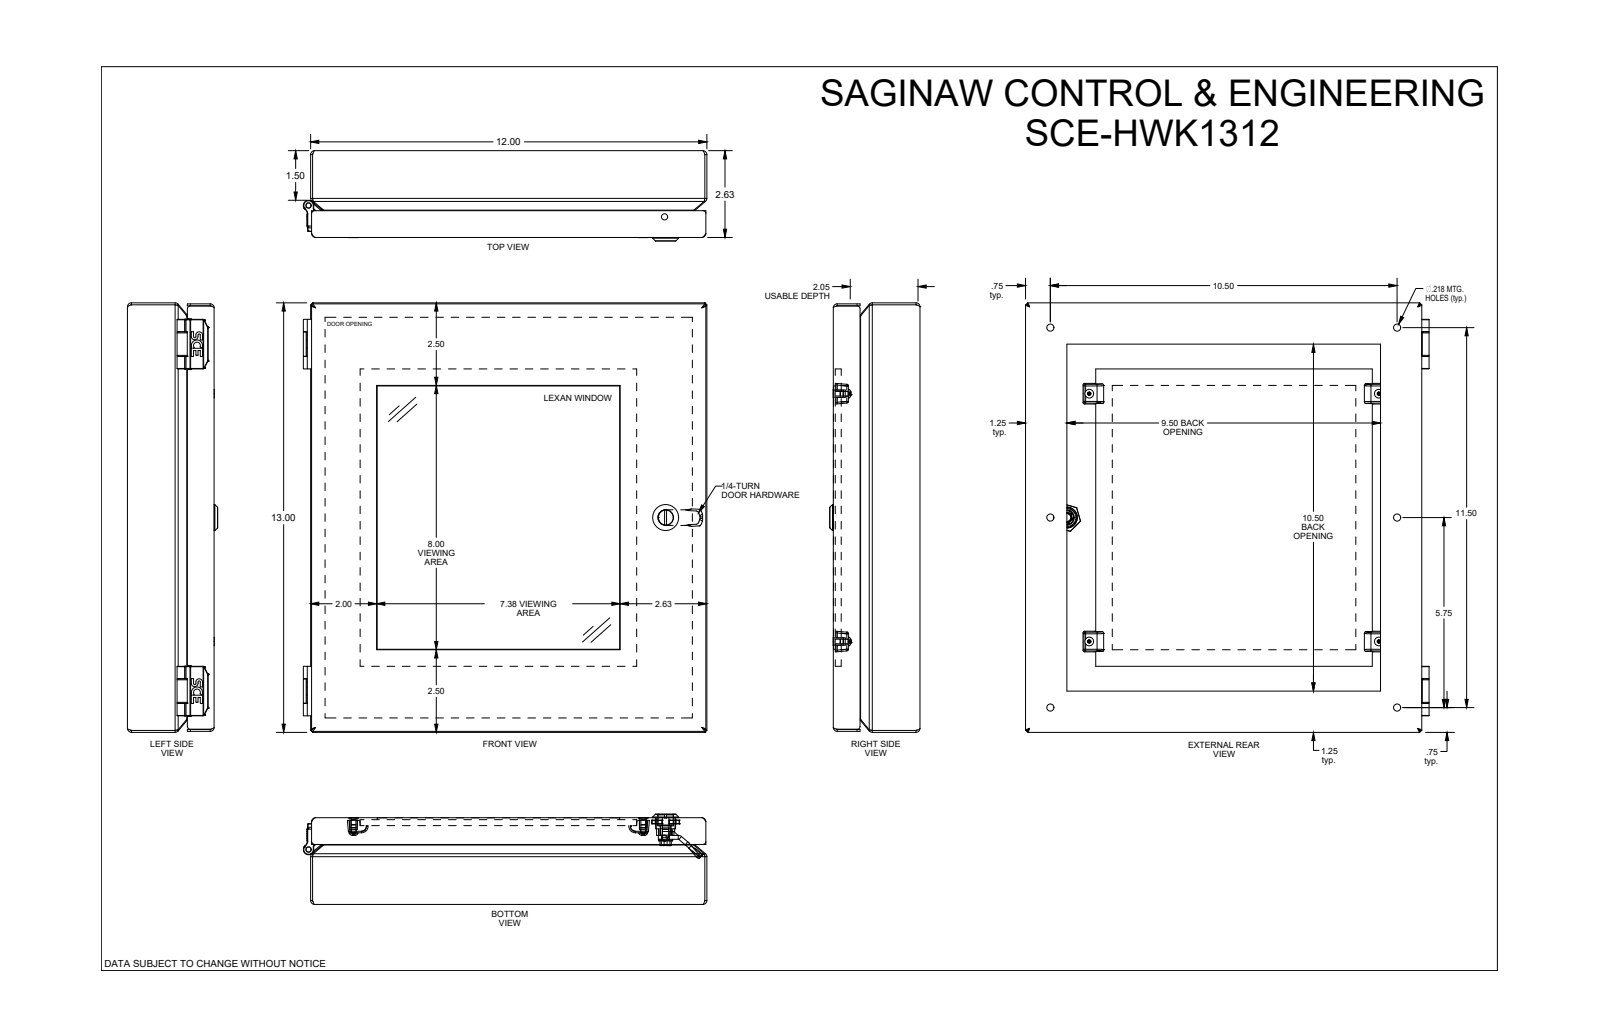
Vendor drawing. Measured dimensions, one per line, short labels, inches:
name: SCE-HWK1312
written by: SolidWorks 2021 (AUTOMOTIVE_DESIGN)
unit: in
bodies: 33 solids, 1957 faces (548 planar, 597 cylindrical, 812 other)
size: 13.06 × 12.22 × 2.733
volume: 39.59 in³; area: 866.5 in²
holes: 4× ⌀0.138, 4× ⌀0.156, 4× ⌀0.17, 4× ⌀0.218, 1× ⌀0.02, 1× ⌀0.1, 1× ⌀0.158, 1× ⌀0.196, 1× ⌀0.2, 1× ⌀0.239, 1× ⌀0.254, 1× ⌀0.269
bosses: 4× ⌀0.479, 4× ⌀0.262, 4× ⌀0.212, 2× ⌀0.26, 2× ⌀0.18, 1× ⌀0.788, 1× ⌀0.548, 1× ⌀0.46
rounds: 132× R0.106, 72× R0.005, 32× R0.008, 30× R0.05, 28× R0.03, 24× R0.025, 21× R0.013, 14× R0.01
face distances: 0.059, 0.06, 0.181, 0.241, 0.236, 0.055, 2.385, 2.566, 2.62, 2.626
hole spacings: 3.811, 7.5, 8.77, 10.167, 10.5, 10.552, 11.54, 11.552
